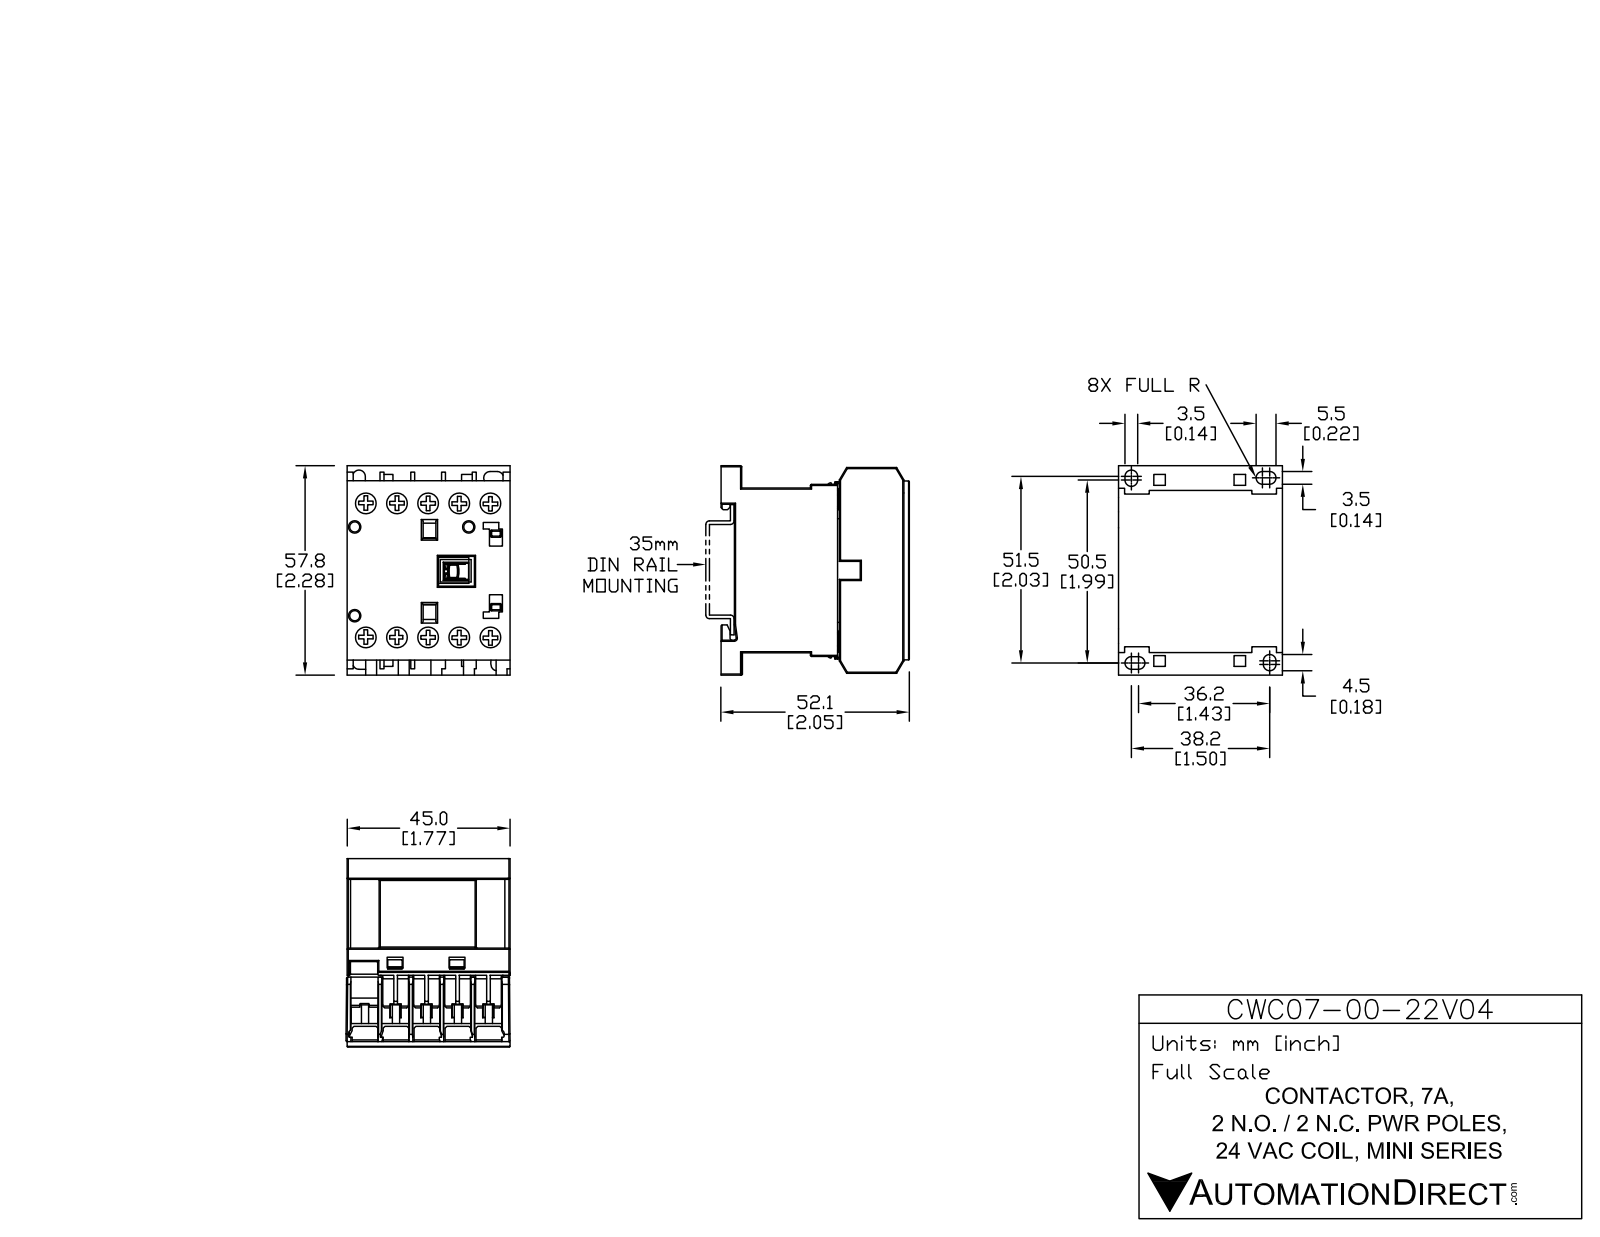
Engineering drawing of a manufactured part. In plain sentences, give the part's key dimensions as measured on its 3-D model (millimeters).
The part is named "CWC07-00-22V04". Its 3-D file was written by "SolidWorks 2013 (AUTOMOTIVE_DESIGN)". It is 15 solids with 535 faces: 445 planar, 90 cylindrical and 0 other. Overall it measures 58.04 by 52.12 by 45.75 millimeters. Its volume is 97 133 cubic millimeters and its surface area 30 437 square millimeters. Round holes: 10 of diameter 6.2, 3 of diameter 2.8. Round bosses or shafts: 10 of diameter 5.9. Partial cylindrical surfaces (rounded edges, fillets, slot ends): 20 of radius 0.3, 6 of radius 1.72, 2 of radius 1.73, 1 of radius 0.32, 1 of radius 0.42, 1 of radius 0.55. The main face-to-face distances are 8.25, 45.5, 1.25, 16.5, 9.5, 5.5, 17.75, 5.13, 10.63, 7. The hole center spacings are 8.55, 37.94, 17.1, 40.72, 36.96, 25.65, 44.99, 6.91.
